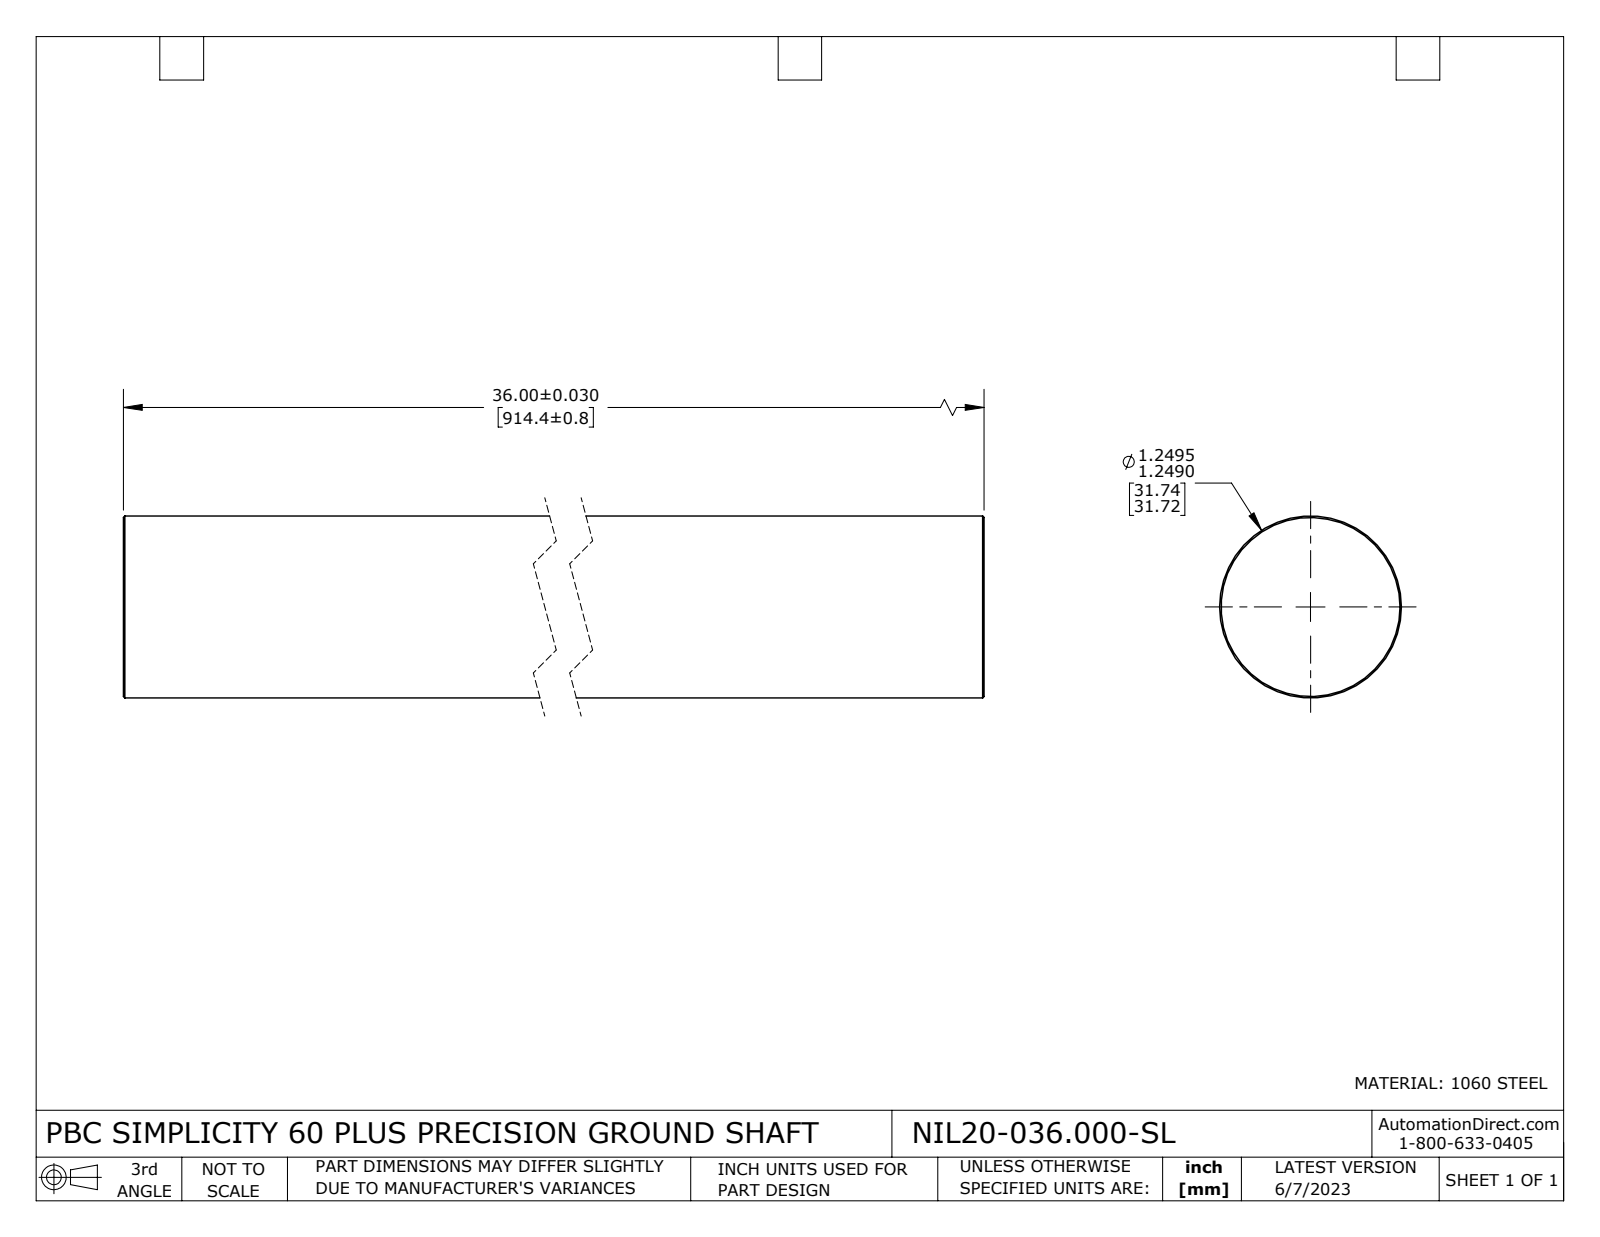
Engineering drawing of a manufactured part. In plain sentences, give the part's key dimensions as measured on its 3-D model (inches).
The part is named "NIL20-036.000-SL". Its 3-D file was written by "SolidWorks 2021 (CONFIG_CONTROL_DESIGN)". It is 1 solid with 8 faces: 2 planar, 2 cylindrical and 4 other. Overall it measures 36 by 1.25 by 1.25 inches. Its volume is 44.18 cubic inches and its surface area 143.8 square inches. Round bosses or shafts: 1 of diameter 1.25. The main face-to-face distances are 36.
